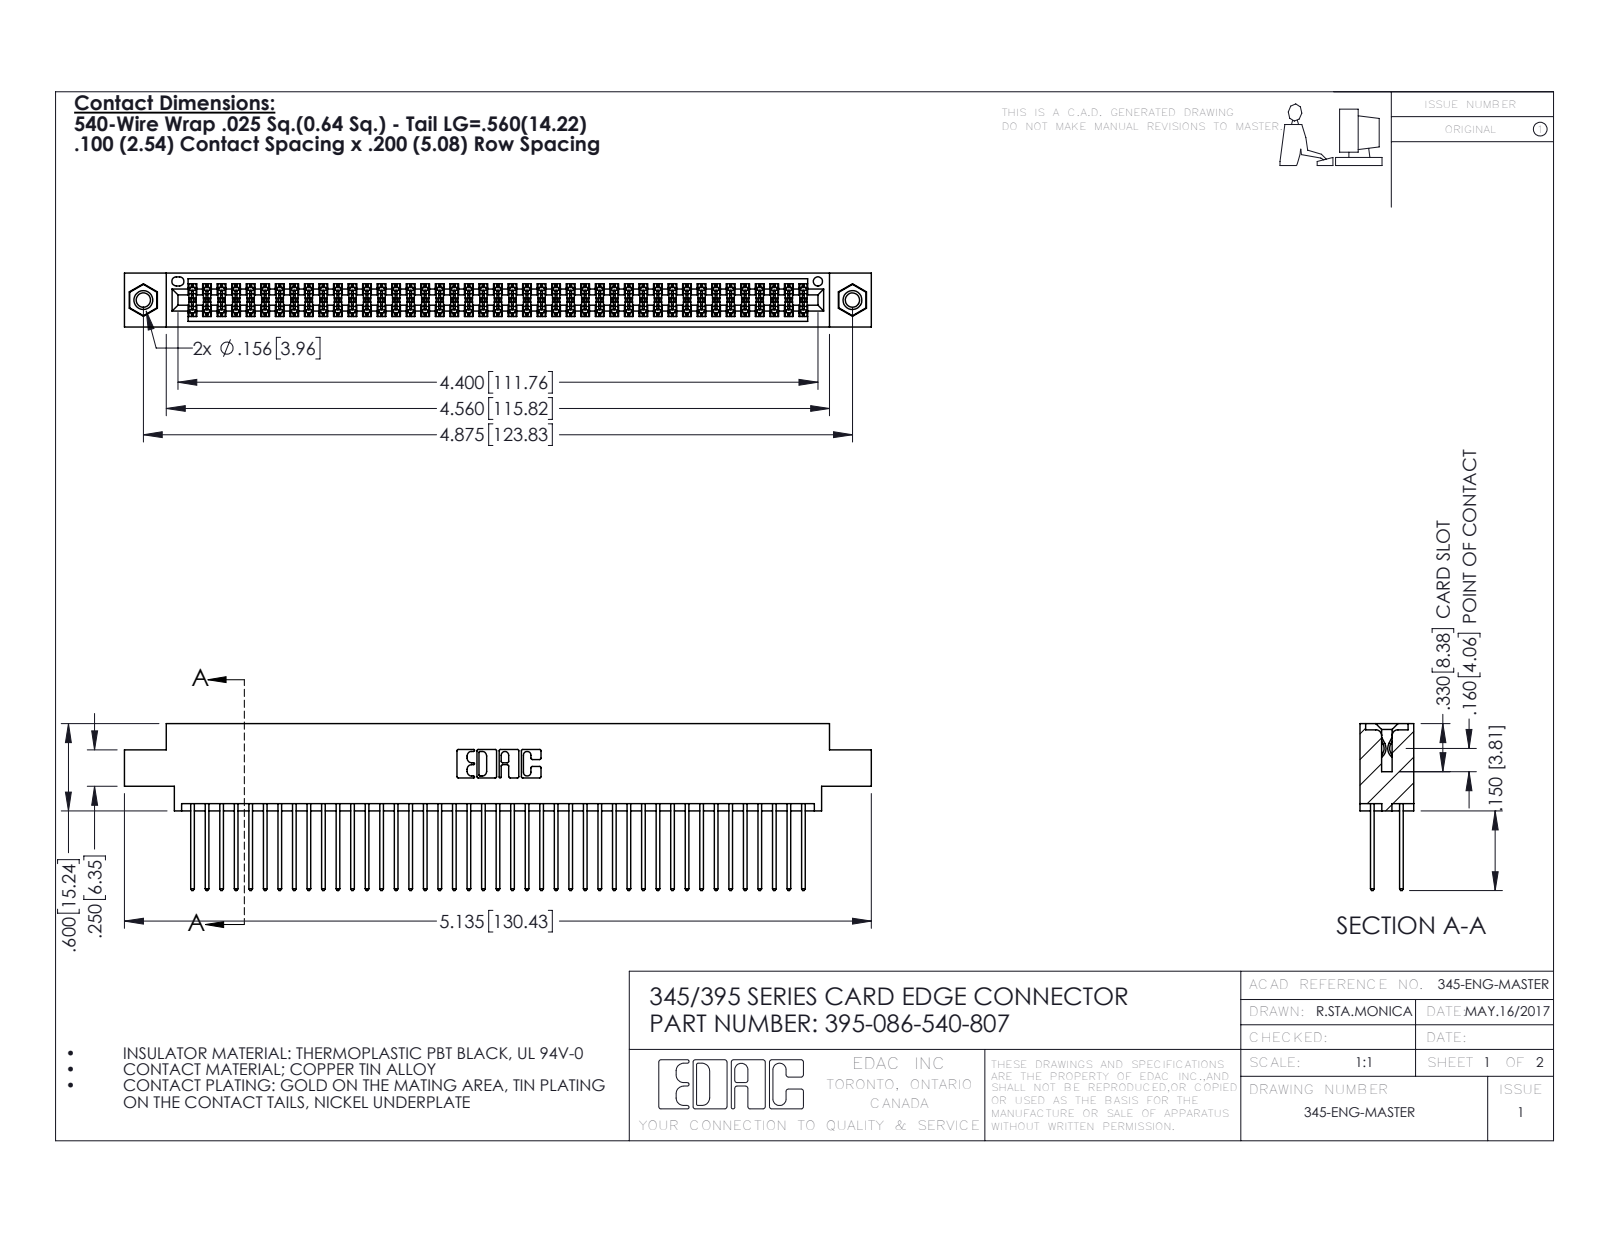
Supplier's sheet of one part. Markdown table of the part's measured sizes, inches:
| quantity | value |
| --- | --- |
| part name | 345 Part_0.170 Offset - 0.156 Dia-TI; 345-292-001_345-293-140; 345-250-001_345-250-005-103; 395-086-540-807 |
| STEP written by | SolidWorks 2016 (CONFIG_CONTROL_DESIGN) |
| units | inches |
| bodies | 89 solids, 4490 faces (2954 planar, 1520 cylindrical, 16 other) |
| overall size | 5.135 × 1.147 × 0.37 |
| volume | 0.786 in³ |
| surface area | 32.15 in² |
| round holes (diameter × count) | 0.098 × 2, 0.125 × 2, 0.156 × 2, 0.064 × 1 |
| round bosses / shafts (diameter × count) | 0.155 × 2 |
| partial cylindrical surfaces (radius × count) | 0.006 × 129, 0.01 × 86, 0.01 × 22, 0.007 × 6, 0.031 × 6, 0.026 × 3, 0.014 × 2, 0.019 × 2 |
| main face-to-face distances | 0.072, 0.298, 0.2, 0.098, 0.272, 0.025, 0.37, 0.225, 0.175, 0.149 |
| hole center spacings | 0.27, 4.639, 4.875 |
